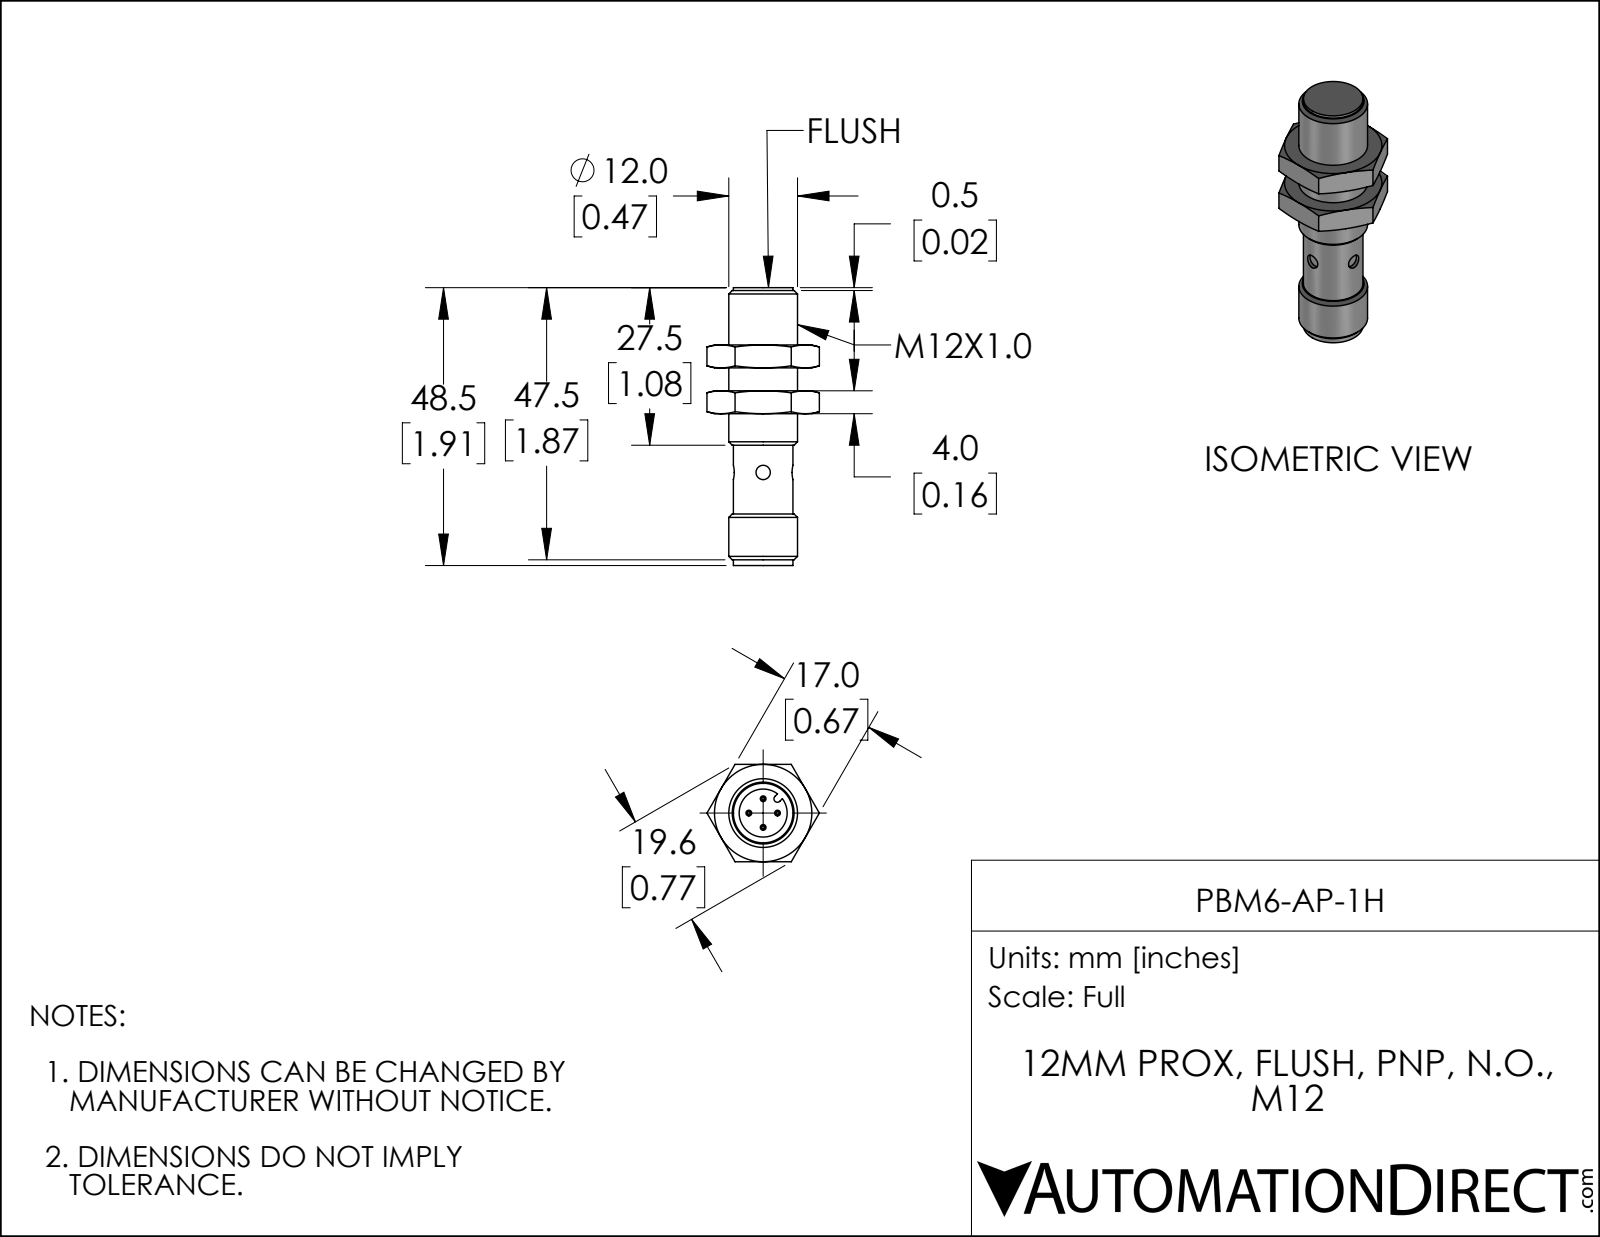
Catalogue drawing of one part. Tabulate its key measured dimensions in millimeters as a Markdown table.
| quantity | value |
| --- | --- |
| part name | DSD-0278 |
| STEP written by | SolidWorks 2019 (AUTOMOTIVE_DESIGN) |
| units | millimeters |
| bodies | 1 solid, 40 faces (17 planar, 15 cylindrical, 8 other) |
| overall size | 48.5 × 12 × 12 |
| volume | 4 600 mm³ |
| surface area | 2 352 mm² |
| round holes (diameter × count) | 2.5 × 2, 8.4 × 1 |
| round bosses / shafts (diameter × count) | 1 × 4, 12 × 1, 10.4 × 1 |
| partial cylindrical surfaces (radius × count) | 0.6 × 1 |
| main face-to-face distances | 39.6, 48.5, 8.9, 9, 0.5, 39.5, 39, 39.1, 48, 27.5 |
